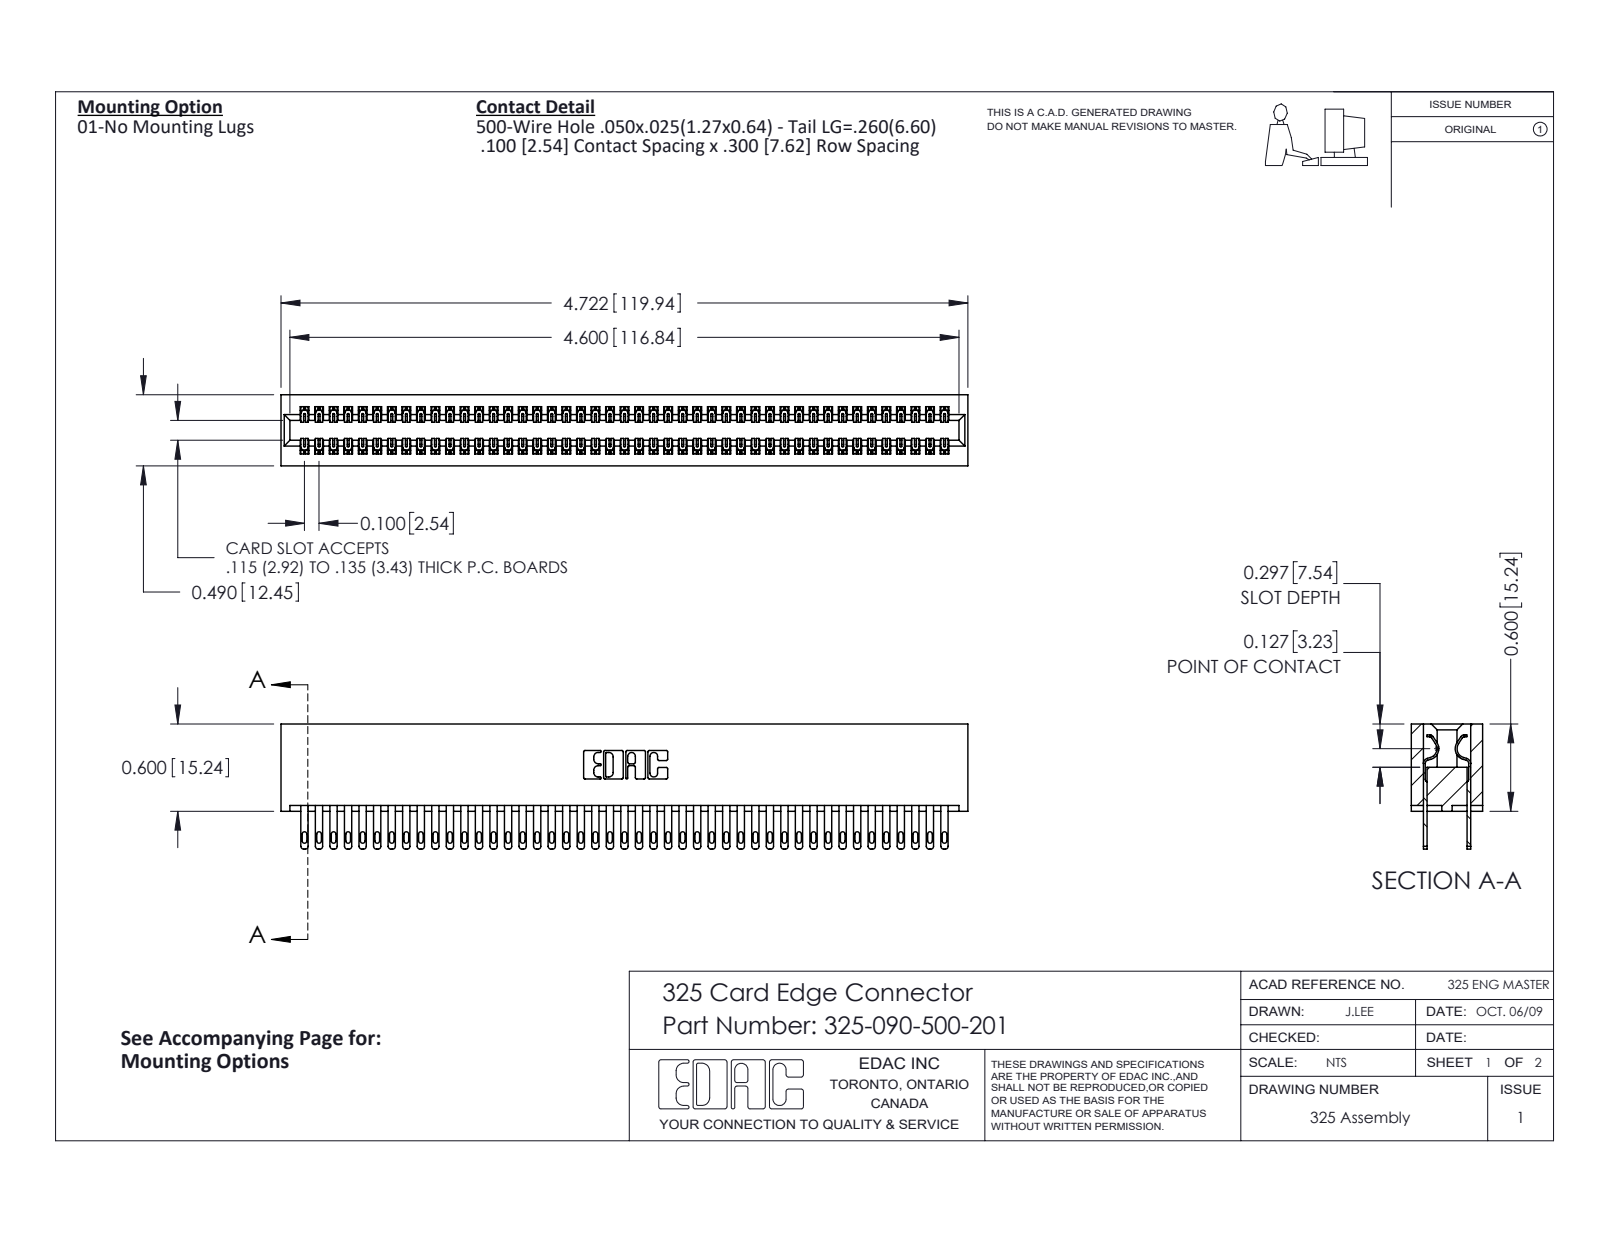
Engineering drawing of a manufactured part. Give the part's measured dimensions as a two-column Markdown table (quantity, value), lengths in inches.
| quantity | value |
| --- | --- |
| part name | 325-090-500-201; 325 Part_Lugless; 325-292-001_325-293-100 |
| STEP written by | SolidWorks 2016 (CONFIG_CONTROL_DESIGN) |
| units | inches |
| bodies | 91 solids, 4426 faces (2766 planar, 1660 cylindrical, 0 other) |
| overall size | 4.722 × 0.86 × 0.49 |
| volume | 1 in³ |
| surface area | 33.35 in² |
| partial cylindrical surfaces (radius × count) | 0.006 × 135, 0.016 × 90, 0.02 × 90, 0.01 × 22, 0.007 × 6, 0.031 × 6, 0.026 × 3, 0.014 × 2 |
| main face-to-face distances | 0.083, 0.407, 0.3, 0.107, 0.383, 0.025, 0.325, 0.49, 0.275, 0.56 |
